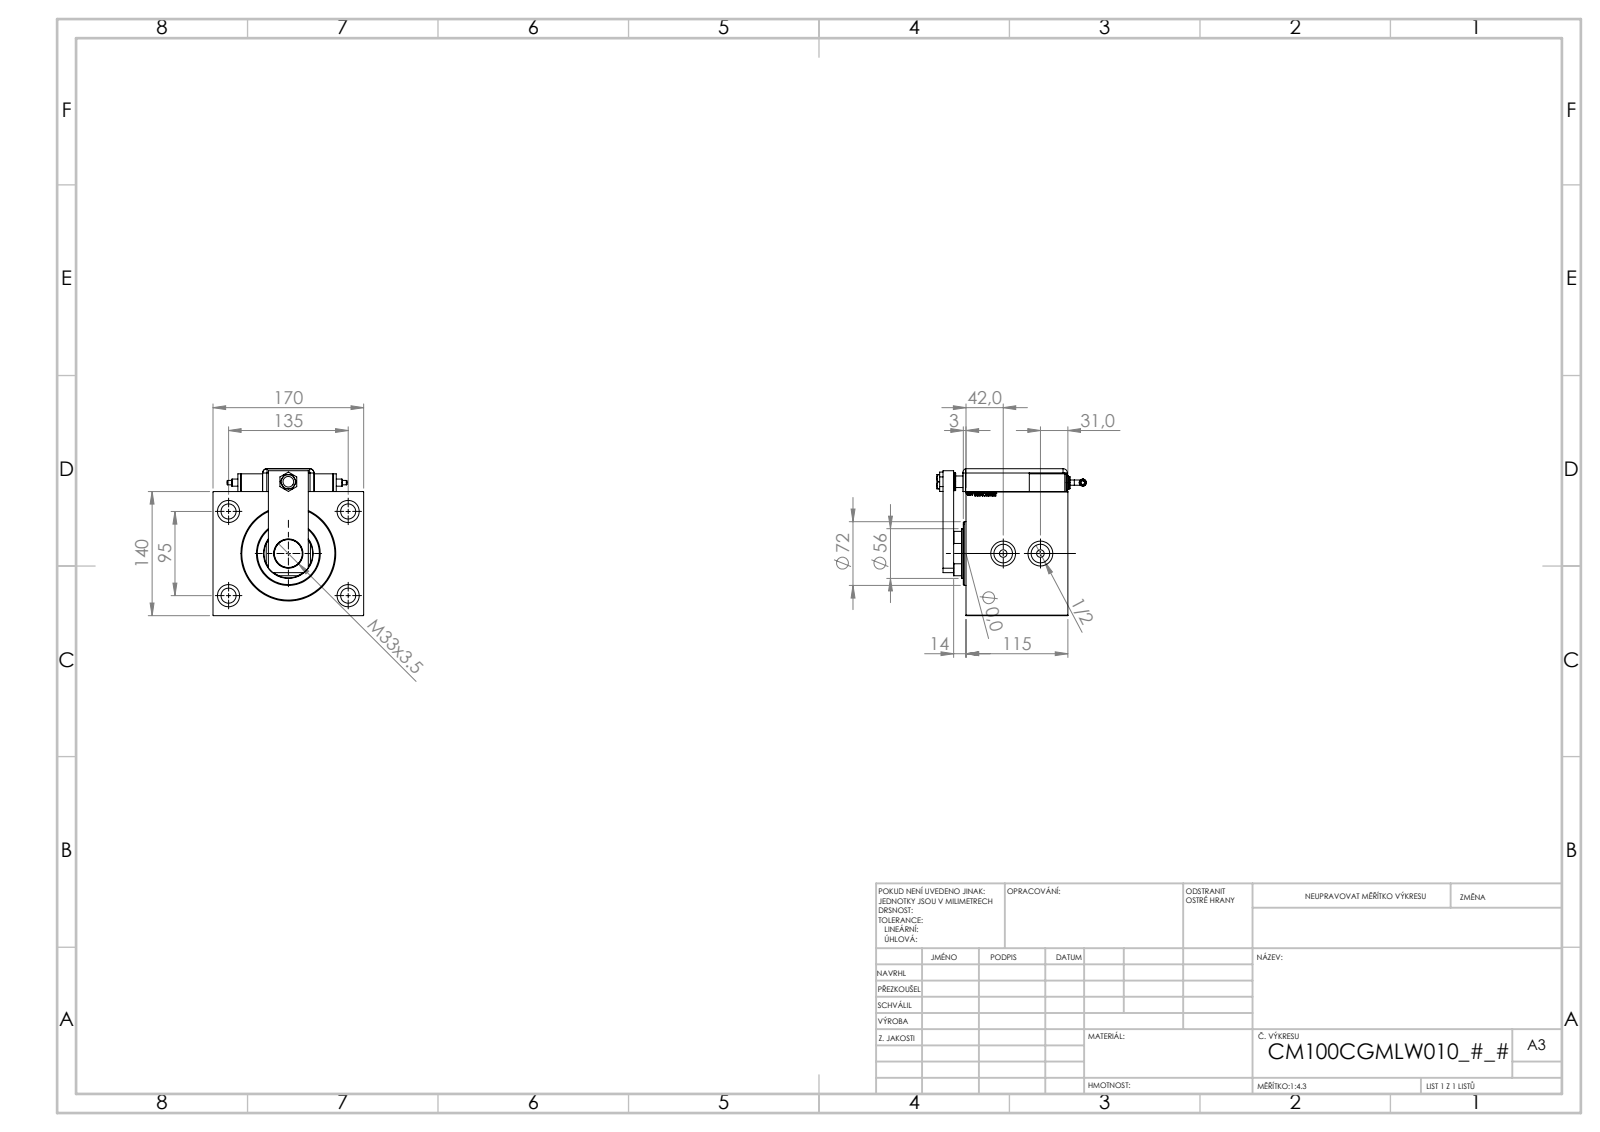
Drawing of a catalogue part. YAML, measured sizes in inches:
part_name: "KRYT; SWITCH DIM A_G; NUT_D13; V450CM_C_Body (+7 more)"
step_written_by: "SolidWorks 2019 (CONFIG_CONTROL_DESIGN)"
units: inches
bodies: {solids: 13, faces: 1275, planar: 619, cylindrical: 123, other: 533}
overall_size: [6.693, 6.64, 6.528]
volume: 165.9
surface_area: 449.4
round_holes:
  - {diameter: 0.669, count: 4}
  - {diameter: 0.984, count: 4}
  - {diameter: 0.157, count: 2}
  - {diameter: 0.315, count: 2}
  - {diameter: 0.335, count: 2}
  - {diameter: 0.825, count: 2}
  - {diameter: 1.102, count: 2}
  - {diameter: 0.472, count: 1}
  - {diameter: 0.512, count: 1}
  - {diameter: 0.551, count: 1}
  - {diameter: 1.24, count: 1}
  - {diameter: 1.299, count: 1}
round_bosses_or_shafts:
  - {diameter: 0.787, count: 3}
  - {diameter: 0.63, count: 2}
  - {diameter: 0.551, count: 2}
  - {diameter: 0.315, count: 2}
  - {diameter: 0.236, count: 2}
  - {diameter: 0.198, count: 2}
  - {diameter: 2.835, count: 1}
partial_cylinders:
  - {radius: 0.197, count: 9}
  - {radius: 0.394, count: 1}
  - {radius: 1.083, count: 1}
face_to_face_distances: [4.528, 5.512, 2.008, 2.52, 6.693, 0.118, 0.394, 2.559, 0.85, 1.157]
hole_center_spacings: [3.25, 2.967, 3.74, 5.315, 5.715, 6.499, 0.787, 1.654]
